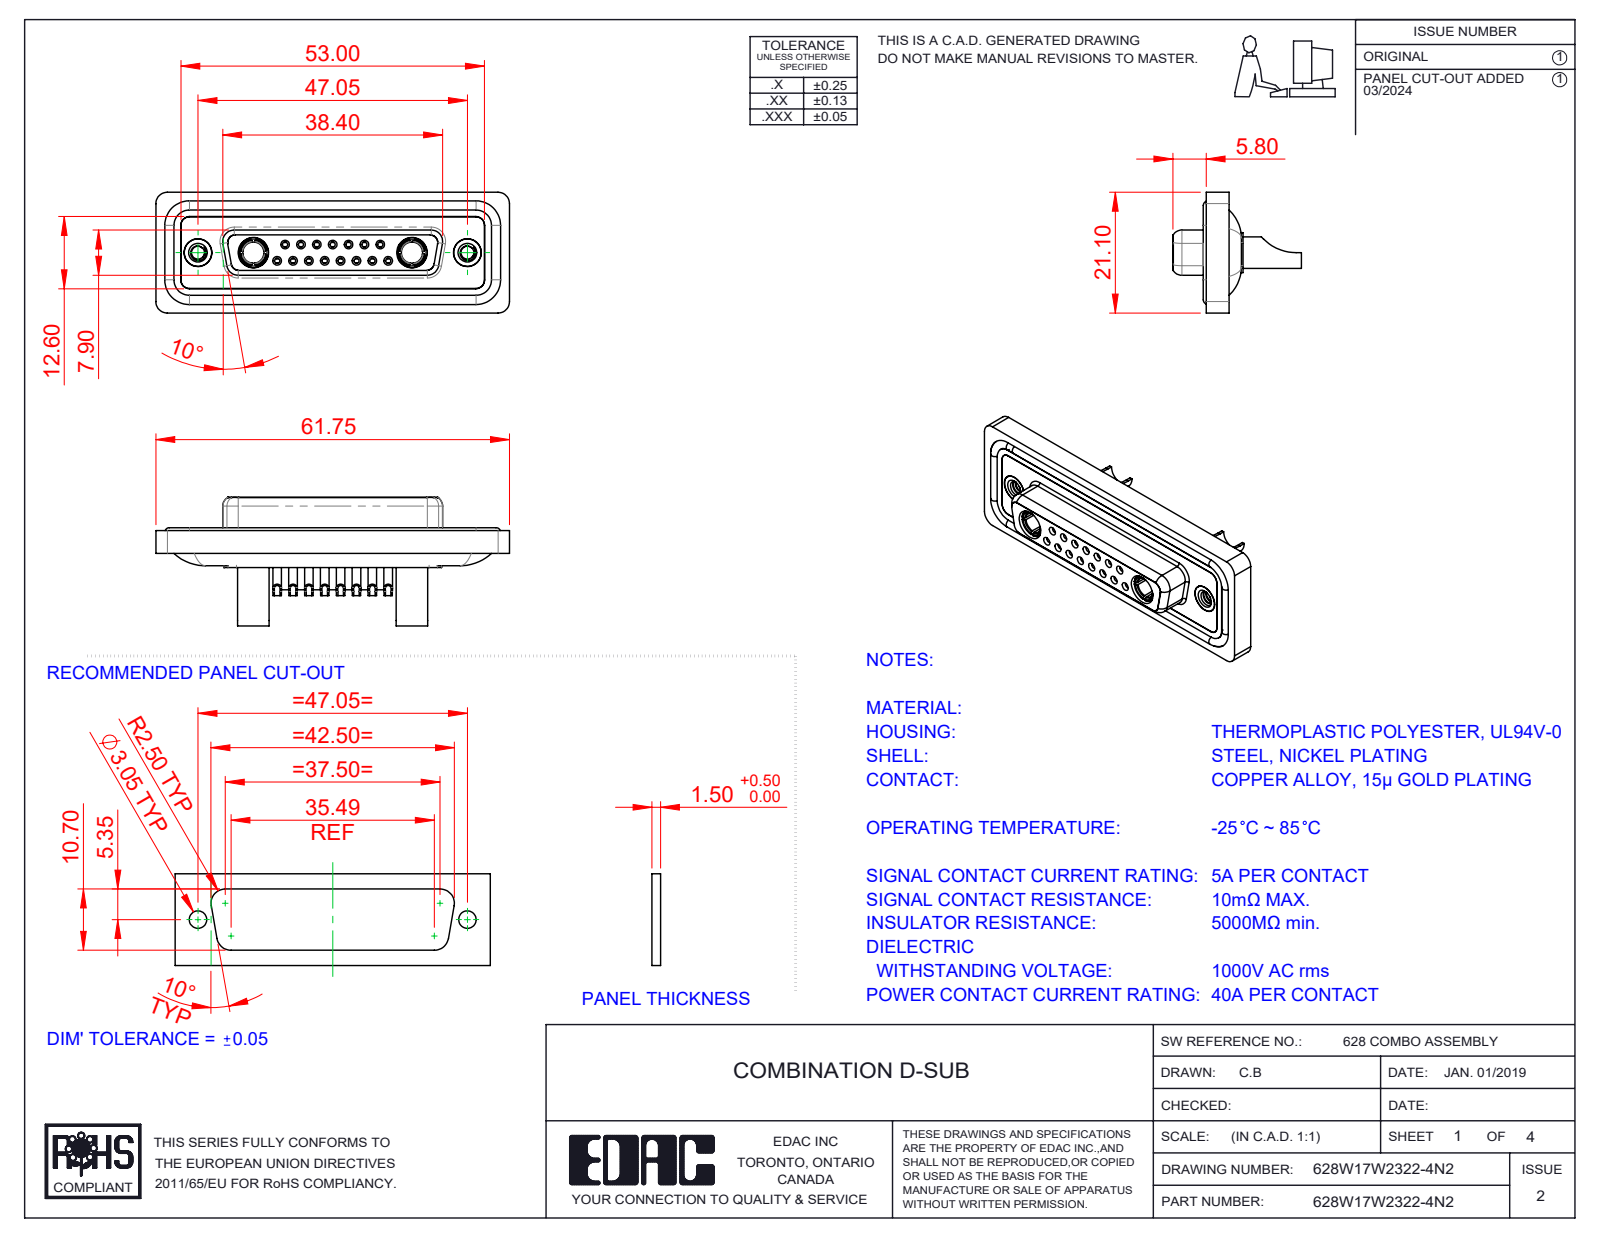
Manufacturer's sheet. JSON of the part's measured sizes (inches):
{"part_name": "628Combo Contact Row 1_22; 628Combo Threaded Rivet_2; 628Combo Shell Rear_25 Contacts; Power Socket_40A SC (+5 more)", "step_written_by": "SolidWorks 2023 (CONFIG_CONTROL_DESIGN)", "units": "inches", "bodies": {"solids": 26, "faces": 1365, "planar": 422, "cylindrical": 551, "other": 392}, "overall_size": [2.431, 0.884, 0.831], "volume_in3": 0.515, "surface_area_in2": 22.16, "round_holes": [[0.035, 15], [0.039, 15], [0.043, 15], [0.059, 15], [0.079, 15], [0.063, 8], [0.067, 7], [0.191, 4], [0.089, 2], [0.146, 2], [0.157, 2], [0.159, 2]], "round_bosses_or_shafts": [[0.087, 15], [0.063, 11], [0.217, 2], [0.205, 2], [0.195, 2], [0.195, 2], [0.189, 2], [0.187, 2]], "partial_cylinders_radius": [[0.059, 22], [0.079, 18], [0.053, 8], [0.063, 8], [0.039, 6], [0.01, 4], [0.02, 4], [0.024, 4]], "face_to_face_distances": [0.016, 0.293, 0.071, 0.222, 0.26, 0.02, 0.278, 0.063, 0.114, 0.043], "hole_center_spacings": [0.124, 0.109, 0.327, 0.218, 0.198, 0.198, 0.295, 0.436]}
